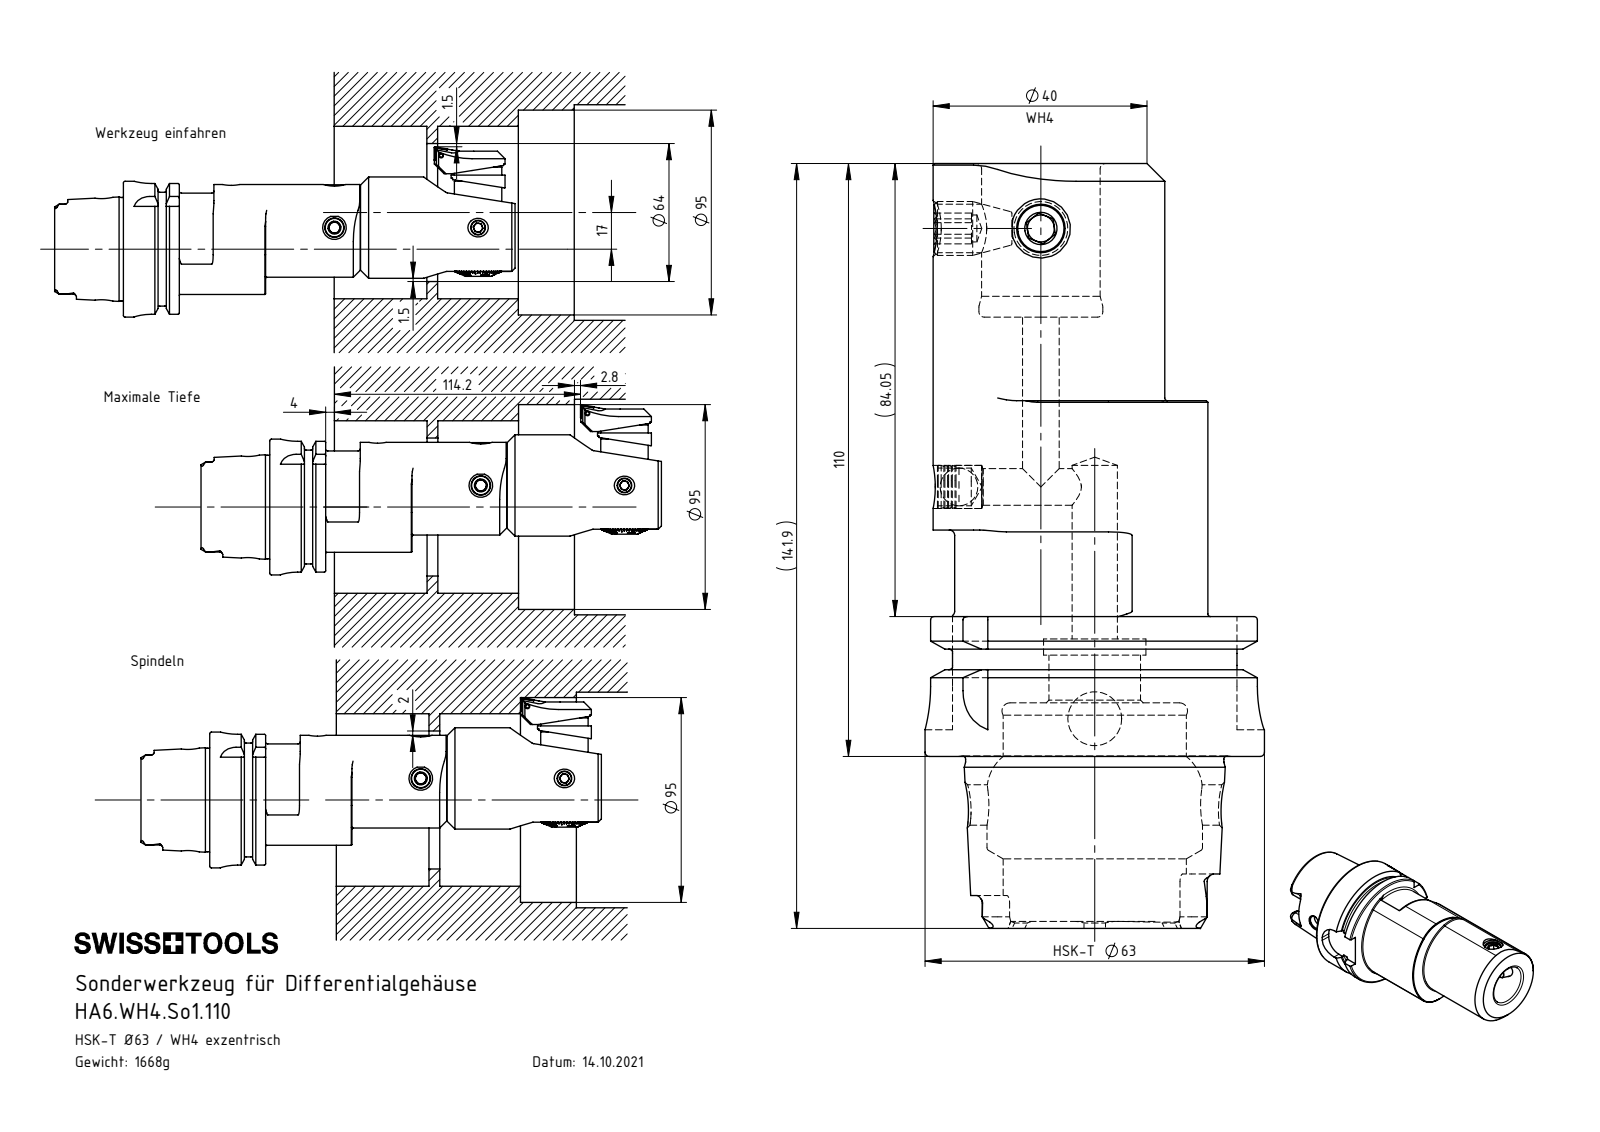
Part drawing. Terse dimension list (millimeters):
name: HA6-WH4.So1.110_A; HA6.WH4.So1.110; KVT_MB_600_080; WH4-ER1.001.015
written by: SolidWorks 2017 (AUTOMOTIVE_DESIGN)
unit: mm
bodies: 5 solids, 237 faces (83 planar, 57 cylindrical, 97 other)
size: 141.9 × 63 × 63
volume: 212 675 mm³; area: 40 629 mm²
holes: 2× ⌀5, 2× ⌀6.8, 2× ⌀9, 1× ⌀7, 1× ⌀7.5, 1× ⌀8.4, 1× ⌀10, 1× ⌀11, 1× ⌀17, 1× ⌀19, 1× ⌀22, 1× ⌀23
bosses: 2× ⌀10, 1× ⌀63, 1× ⌀54.95, 1× ⌀47.94, 1× ⌀8
rounds: 6× R1.4, 4× R2.88, 4× R8, 4× R16, 2× R0.5, 1× R20, 1× R23, 1× R26
face distances: 25.95, 110, 84.05, 16, 9.95, 100.05, 66, 56.05, 40.05, 44
hole spacings: 10, 47.95, 59, 91.5, 106.95
